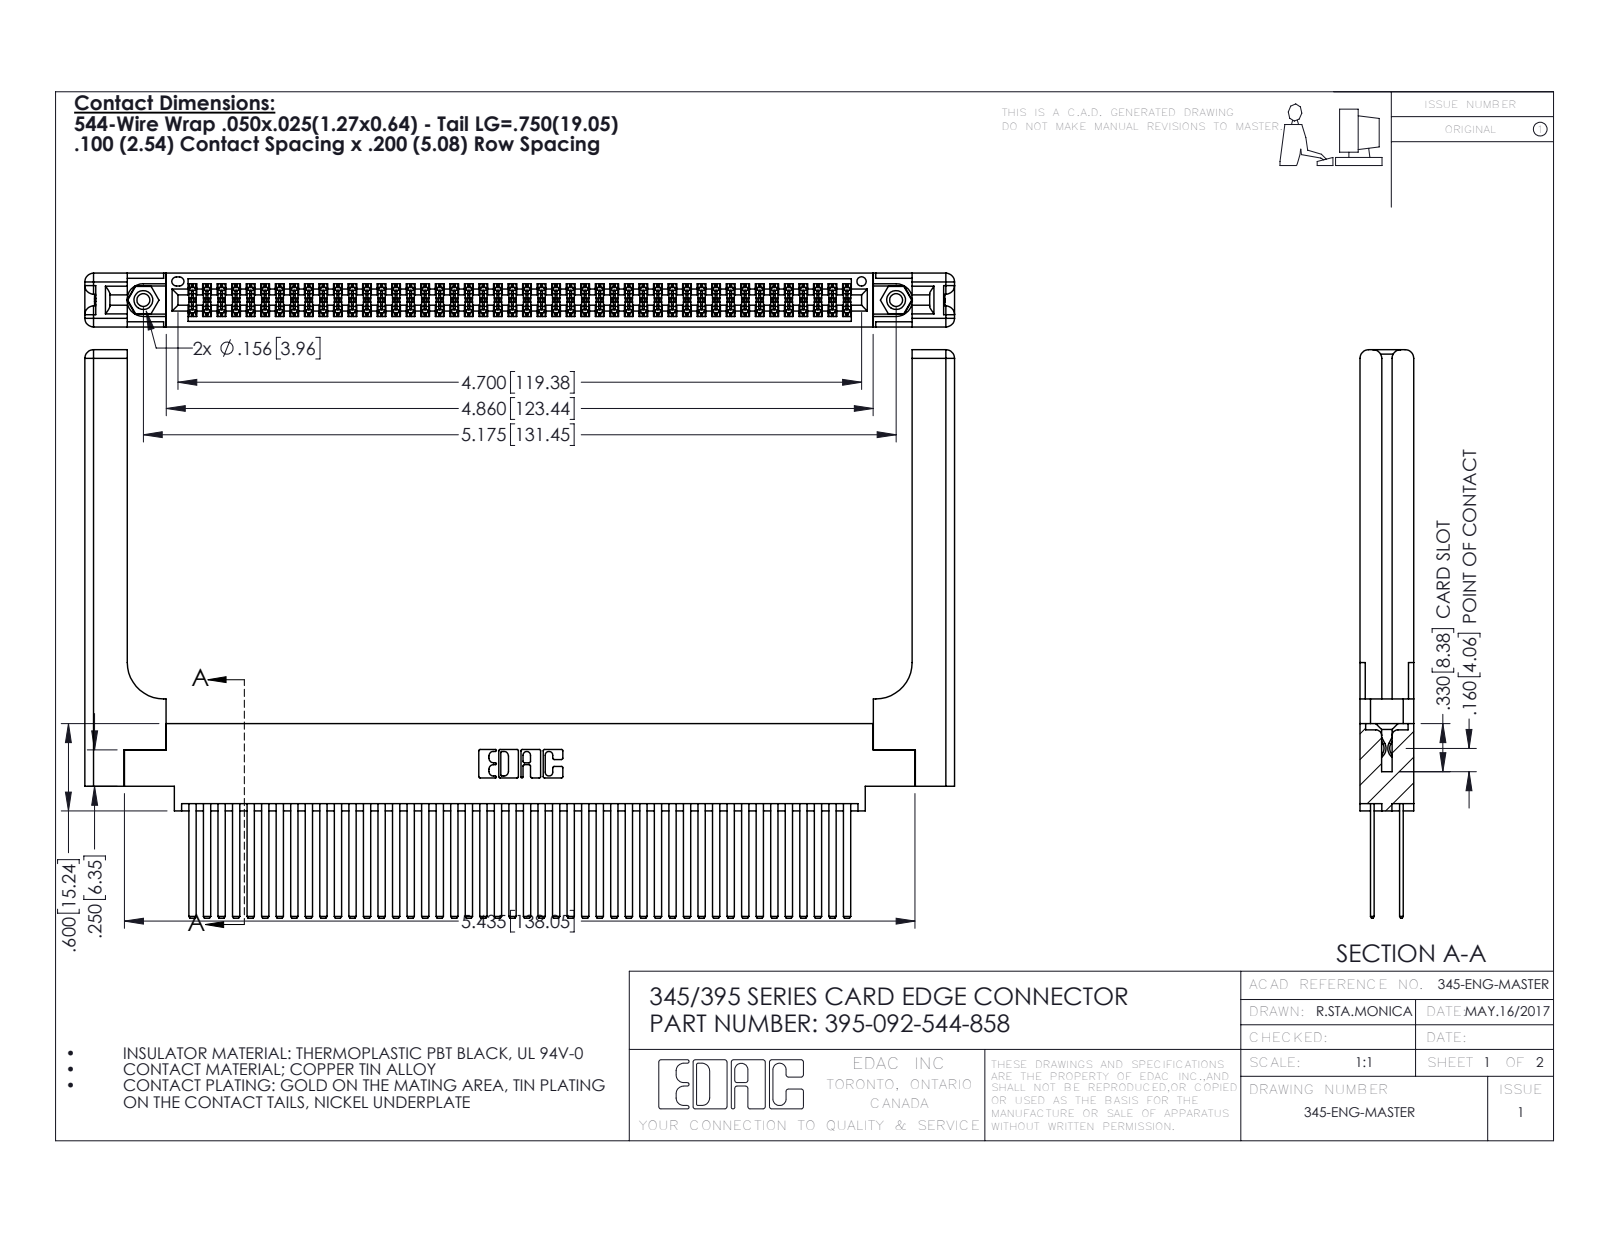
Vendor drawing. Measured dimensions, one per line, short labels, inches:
name: 345 Part_0.170 Offset - 0.156 Dia-TH; 345-220-058_345-220-058; 395-092-544-858; 345-292-001_345-293-144 (+1 more)
written by: SolidWorks 2016 (CONFIG_CONTROL_DESIGN)
unit: in
bodies: 97 solids, 4434 faces (2900 planar, 1474 cylindrical, 60 other)
size: 5.979 × 3.907 × 0.37
volume: 1.491 in³; area: 50.62 in²
holes: 2× ⌀0.089, 2× ⌀0.125, 2× ⌀0.156, 1× ⌀0.064
bosses: 2× ⌀0.155
rounds: 138× R0.006, 22× R0.01, 16× R0.06, 6× R0.007, 6× R0.031, 3× R0.026, 2× R0.014, 2× R0.019
face distances: 0.072, 0.298, 0.098, 0.272, 0.025, 0.2, 0.37, 0.225, 0.175, 0.148
hole spacings: 0.27, 4.939, 5.175
